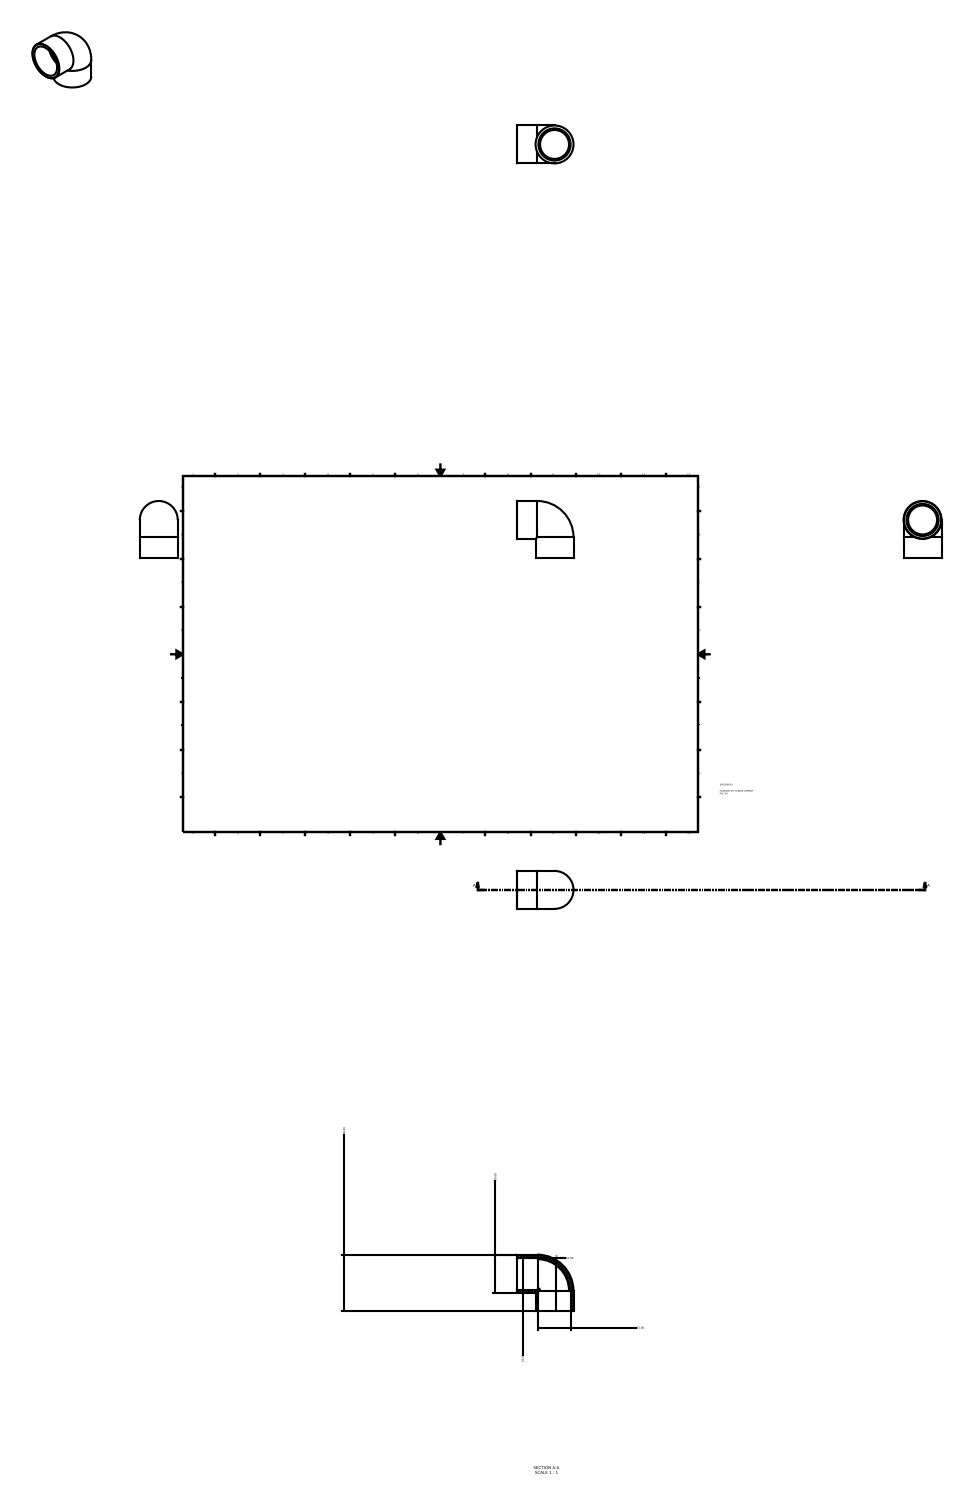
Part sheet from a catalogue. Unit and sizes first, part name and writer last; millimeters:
Units: millimetres
Overall size (bounding box): 88 × 88 × 59
Round holes (diameter × count): ⌀50 ×2
Round bosses / shafts (diameter × count): ⌀59 ×2
Main face-to-face distances: 32
Volume: 97 654 mm³ · Surface area: 37 721 mm²
Bodies: 1 solid, 11 faces (4 planar, 4 cylindrical, 3 other)
Part name (STEP PRODUCT): 050500050
STEP written by: Autodesk Inventor 2015 (AUTOMOTIVE_DESIGN)
